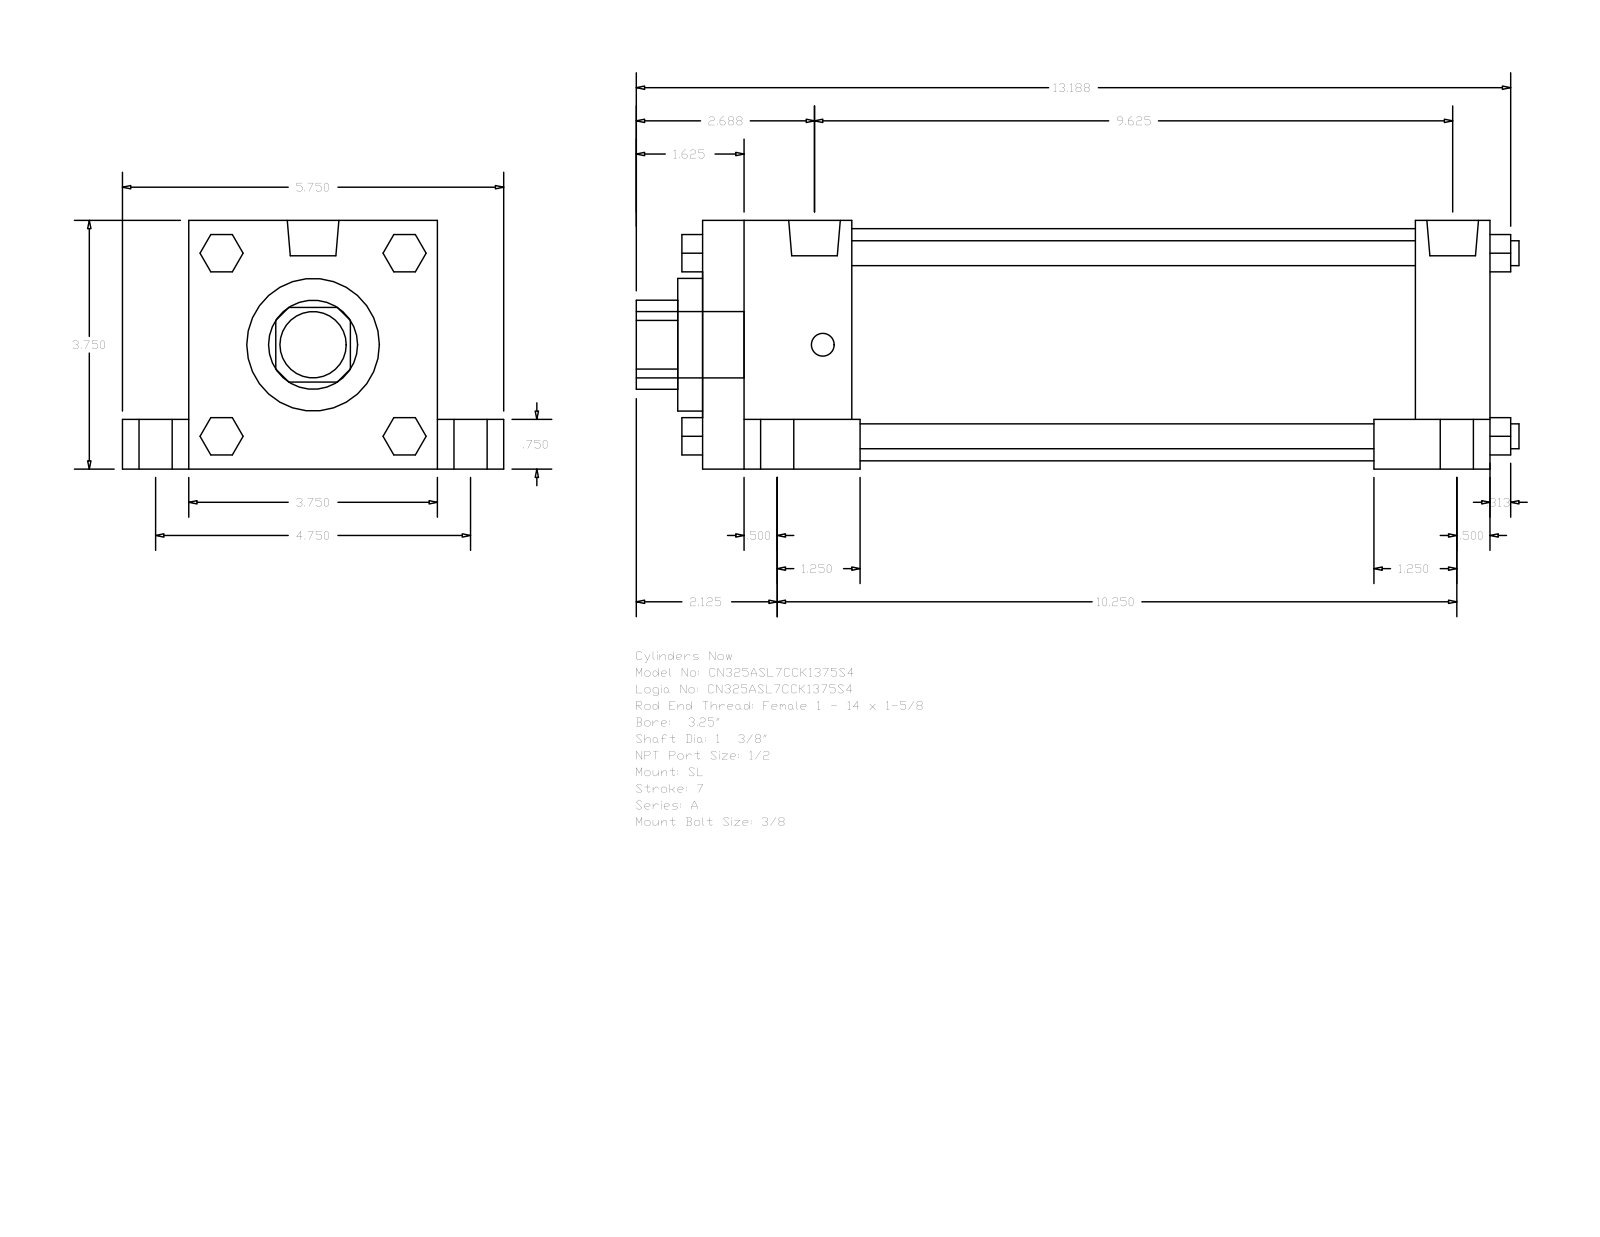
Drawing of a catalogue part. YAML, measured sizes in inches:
part_name: "A_SL__0325_1.375"
step_written_by: "GSSL Pune (CONFIG_CONTROL_DESIGN)"
units: inches
bodies: {solids: 0, faces: 150, planar: 114, cylindrical: 36, other: 0}
overall_size: [13.313, 5.75, 3.75]
round_holes:
  - {diameter: 1.375, count: 1}
  - {diameter: 2, count: 1}
  - {diameter: 3.5, count: 1}
round_bosses_or_shafts:
  - {diameter: 0.75, count: 4}
  - {diameter: 0.5, count: 4}
  - {diameter: 0.375, count: 4}
  - {diameter: 0.344, count: 4}
  - {diameter: 0.778, count: 2}
  - {diameter: 1, count: 1}
partial_cylinders:
  - {radius: 0.672, count: 1}
face_to_face_distances: [3.75, 11.875, 1, 4.75, 0.75, 3, 1.125, 2.25, 10.75, 8.5]
